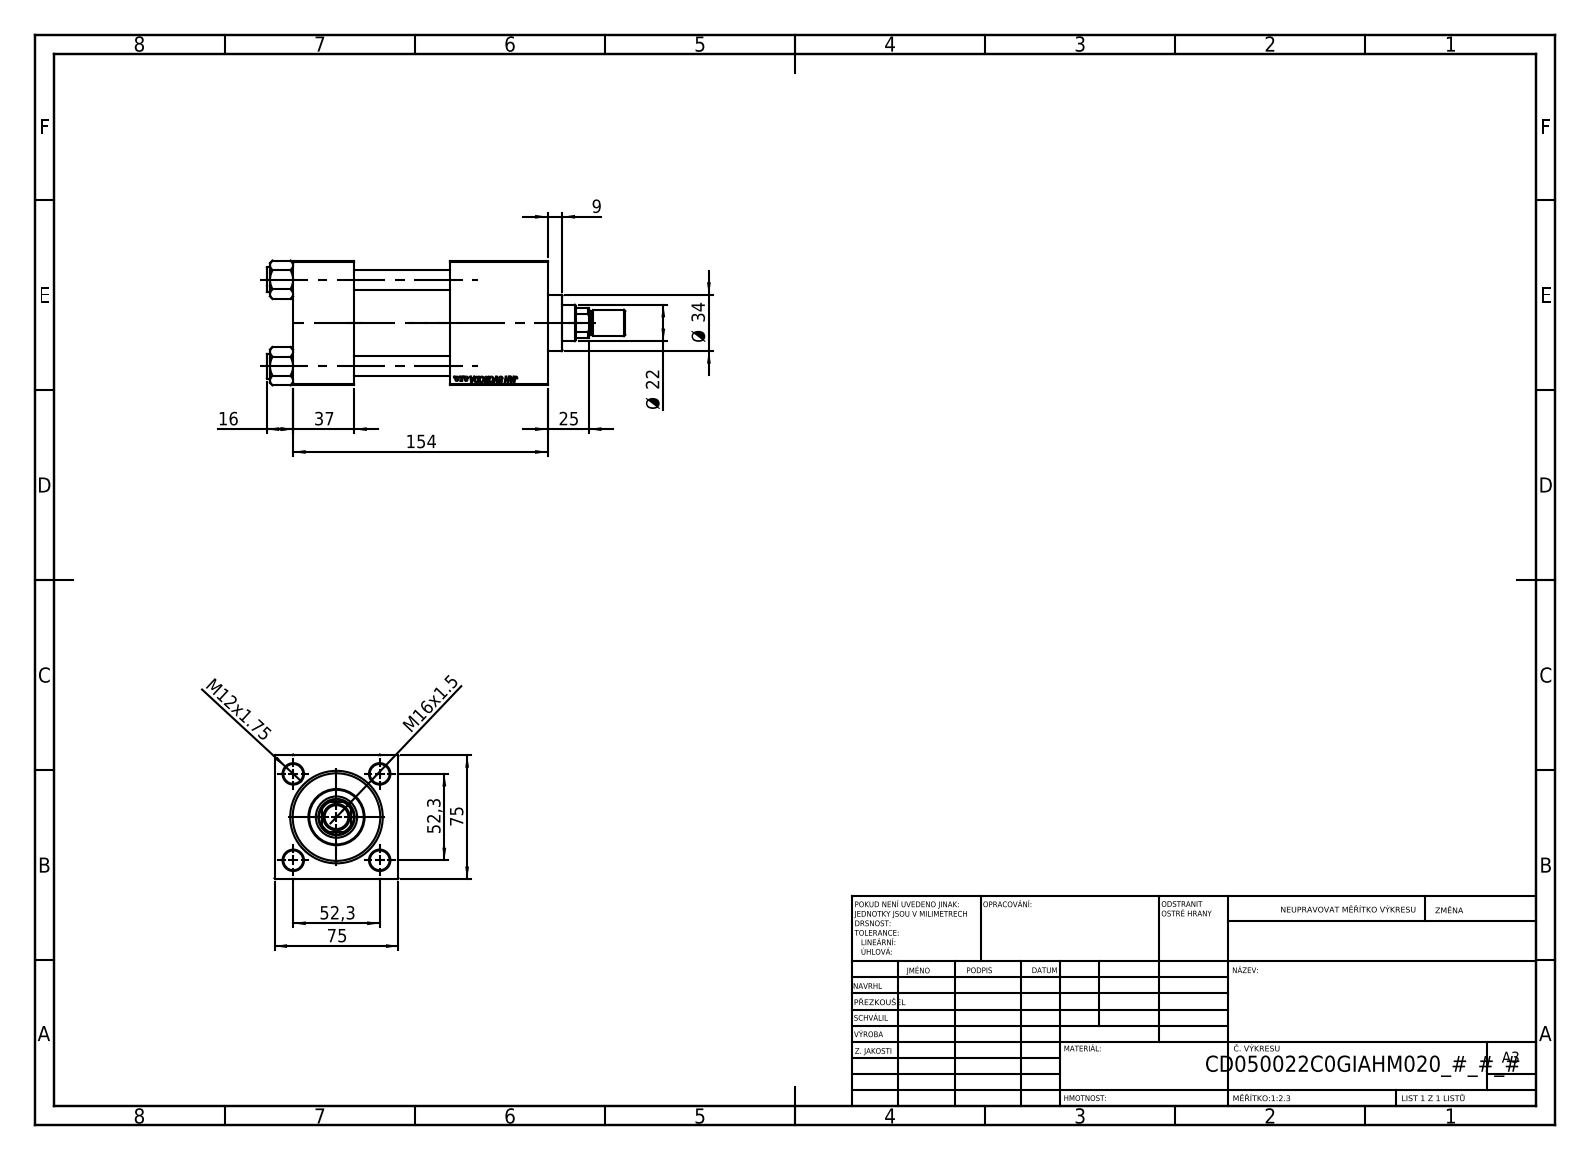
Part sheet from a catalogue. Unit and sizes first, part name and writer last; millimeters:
Units: millimetres
Overall size (bounding box): 217 × 75.54 × 75
Round holes (diameter × count): ⌀12 ×4, ⌀7 ×2, ⌀20.96 ×2, ⌀30 ×2, ⌀10.5 ×1, ⌀22 ×1, ⌀25 ×1, ⌀41 ×1, ⌀50 ×1, ⌀53 ×1
Round bosses / shafts (diameter × count): ⌀15 ×4, ⌀56 ×1, ⌀34 ×1, ⌀16 ×1, ⌀14 ×1
Partial cylindrical surfaces — rounded edges, fillets, slot ends (radius × count): R10.5 ×1
Main face-to-face distances: 75, 37, 154, 117, 95, 58, 59, 125.3, 88.3, 30.3
Hole centre spacings: 36.98, 52.3, 73.96
Volume: 661 645 mm³ · Surface area: 148 716 mm²
Bodies: 12 solids, 1162 faces (530 planar, 90 cylindrical, 542 other)
Part name (STEP PRODUCT): NUT_M5_V215CD_C; V215CD_VC_C; V215CD_C_TYCINKA; V215CD_VCP_C (+2 more)
STEP written by: SolidWorks 2019 (CONFIG_CONTROL_DESIGN)
